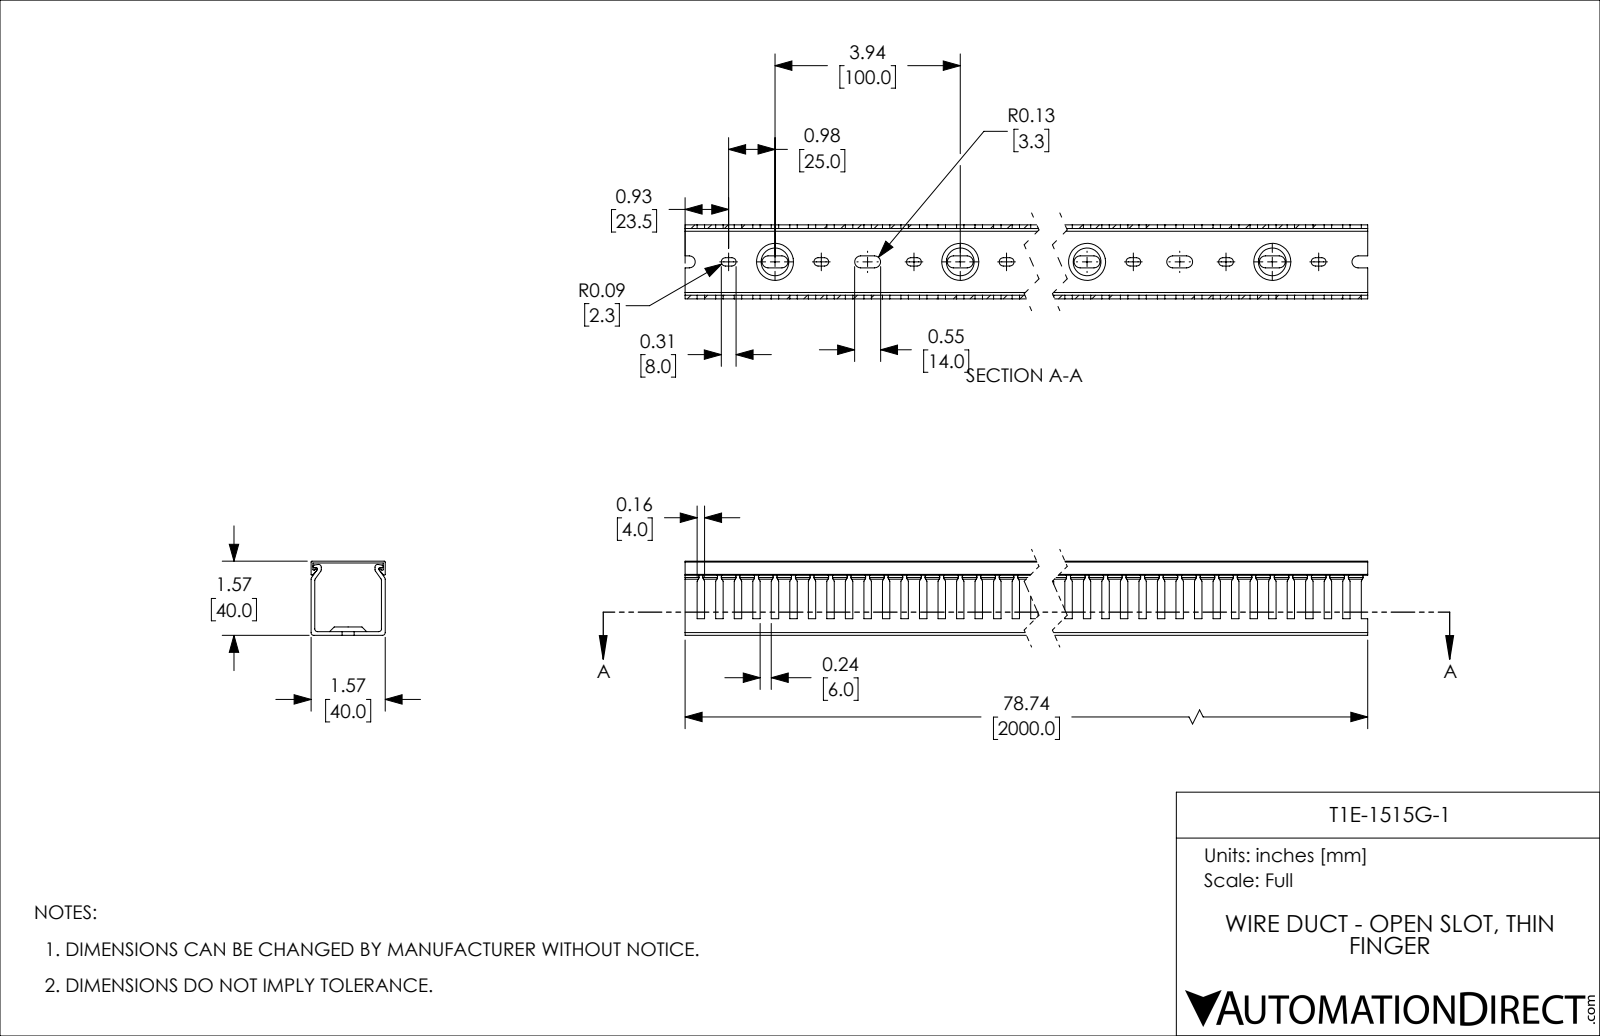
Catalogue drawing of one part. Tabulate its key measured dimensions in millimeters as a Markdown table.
| quantity | value |
| --- | --- |
| part name | T1E-1515G-1 |
| STEP written by | SolidWorks 2021 (CONFIG_CONTROL_DESIGN) |
| units | millimeters |
| bodies | 2 solids, 1005 faces (534 planar, 431 cylindrical, 40 other) |
| overall size | 2000 × 40 × 40 |
| volume | 584 820 mm³ |
| surface area | 699 774 mm² |
| partial cylindrical surfaces (radius × count) | 2.25 × 80, 3.25 × 80, 1.5 × 12, 0.5 × 8, 0.75 × 6 |
| main face-to-face distances | 2, 38, 40, 1, 39, 37, 36, 4.5, 34.5, 5.5 |
